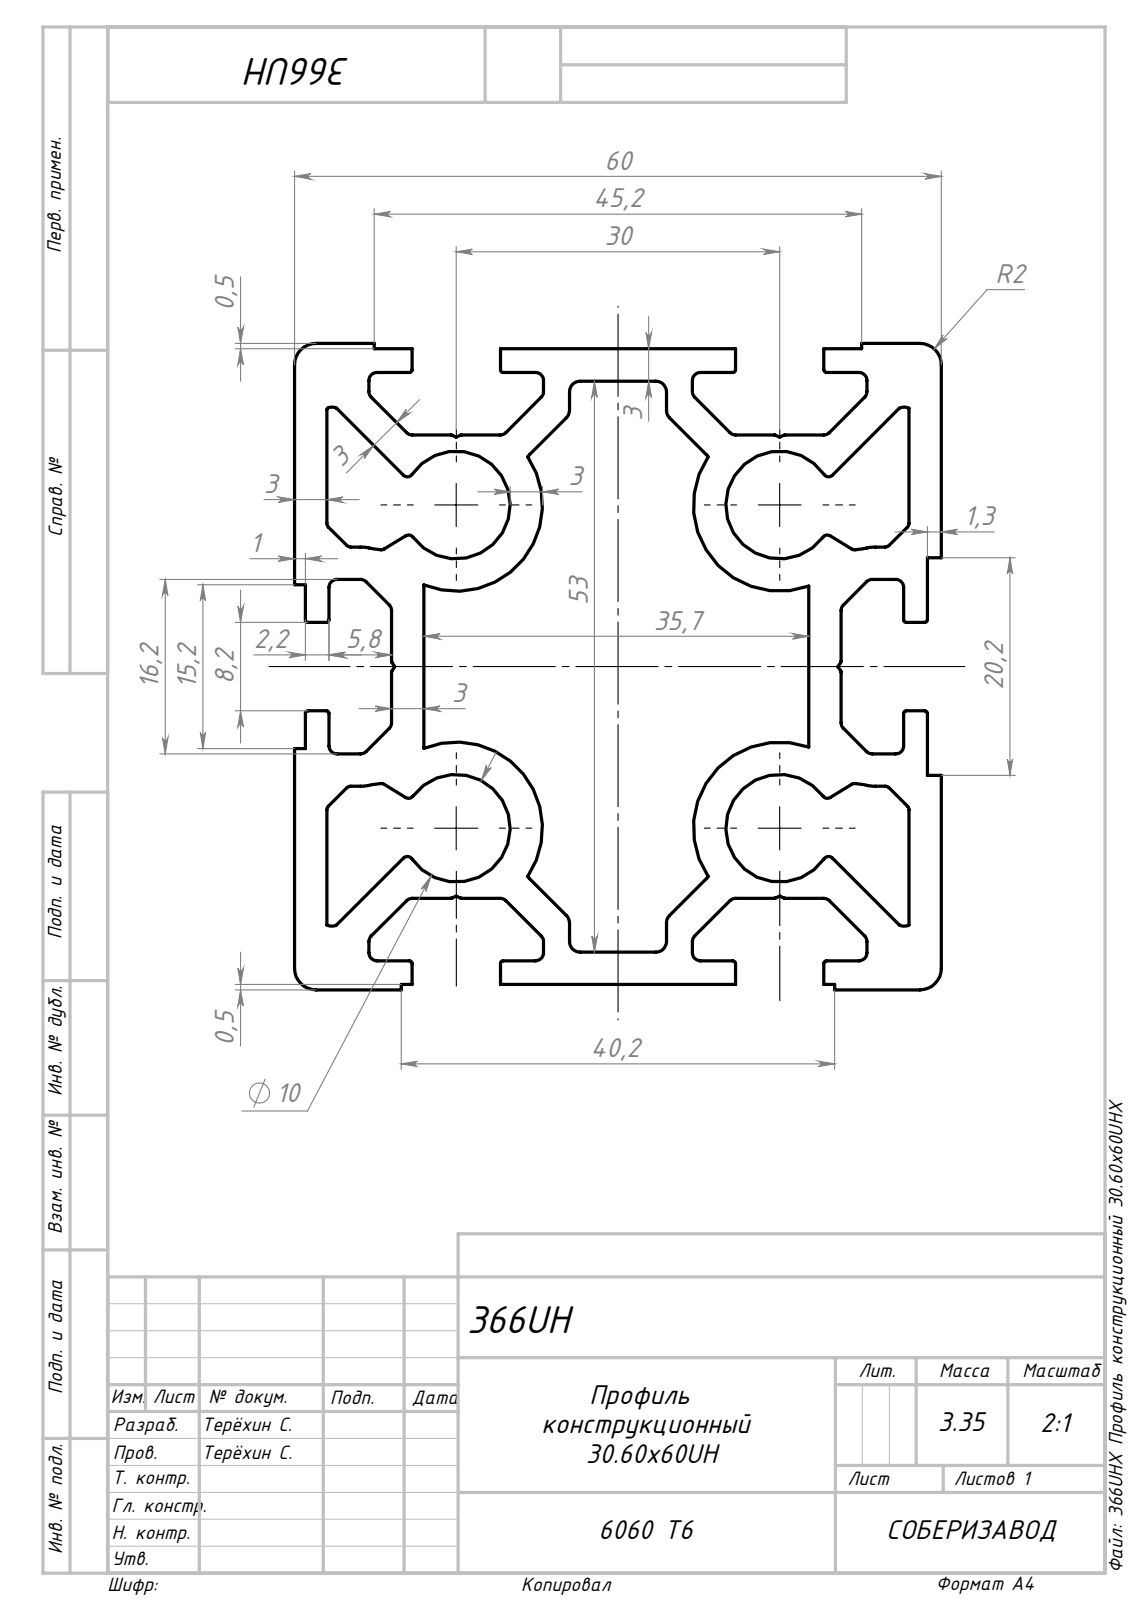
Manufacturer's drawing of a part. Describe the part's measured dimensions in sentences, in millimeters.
The part is named "366SH Конструкционный профиль 60х60SH". Its 3-D file was written by "SolidWorks 2022 (AUTOMOTIVE_DESIGN)". It is 1 solid with 261 faces: 132 planar, 129 cylindrical and 0 other. Overall it measures 1000 by 60 by 60 millimeters. Its volume is 1 243 000 cubic millimeters and its surface area 793 683 square millimeters. Round holes: 4 of diameter 10. Partial cylindrical surfaces (rounded edges, fillets, slot ends): 36 of radius 0.75, 28 of radius 0.25, 20 of radius 0.5, 18 of radius 1, 4 of radius 2, 4 of radius 3.75, 4 of radius 8, 4 of radius 10. The main face-to-face distances are 3, 60, 8, 57, 48, 21.21, 51, 2.2, 5.8, 0.5. The hole center spacings are 30, 42.43.
